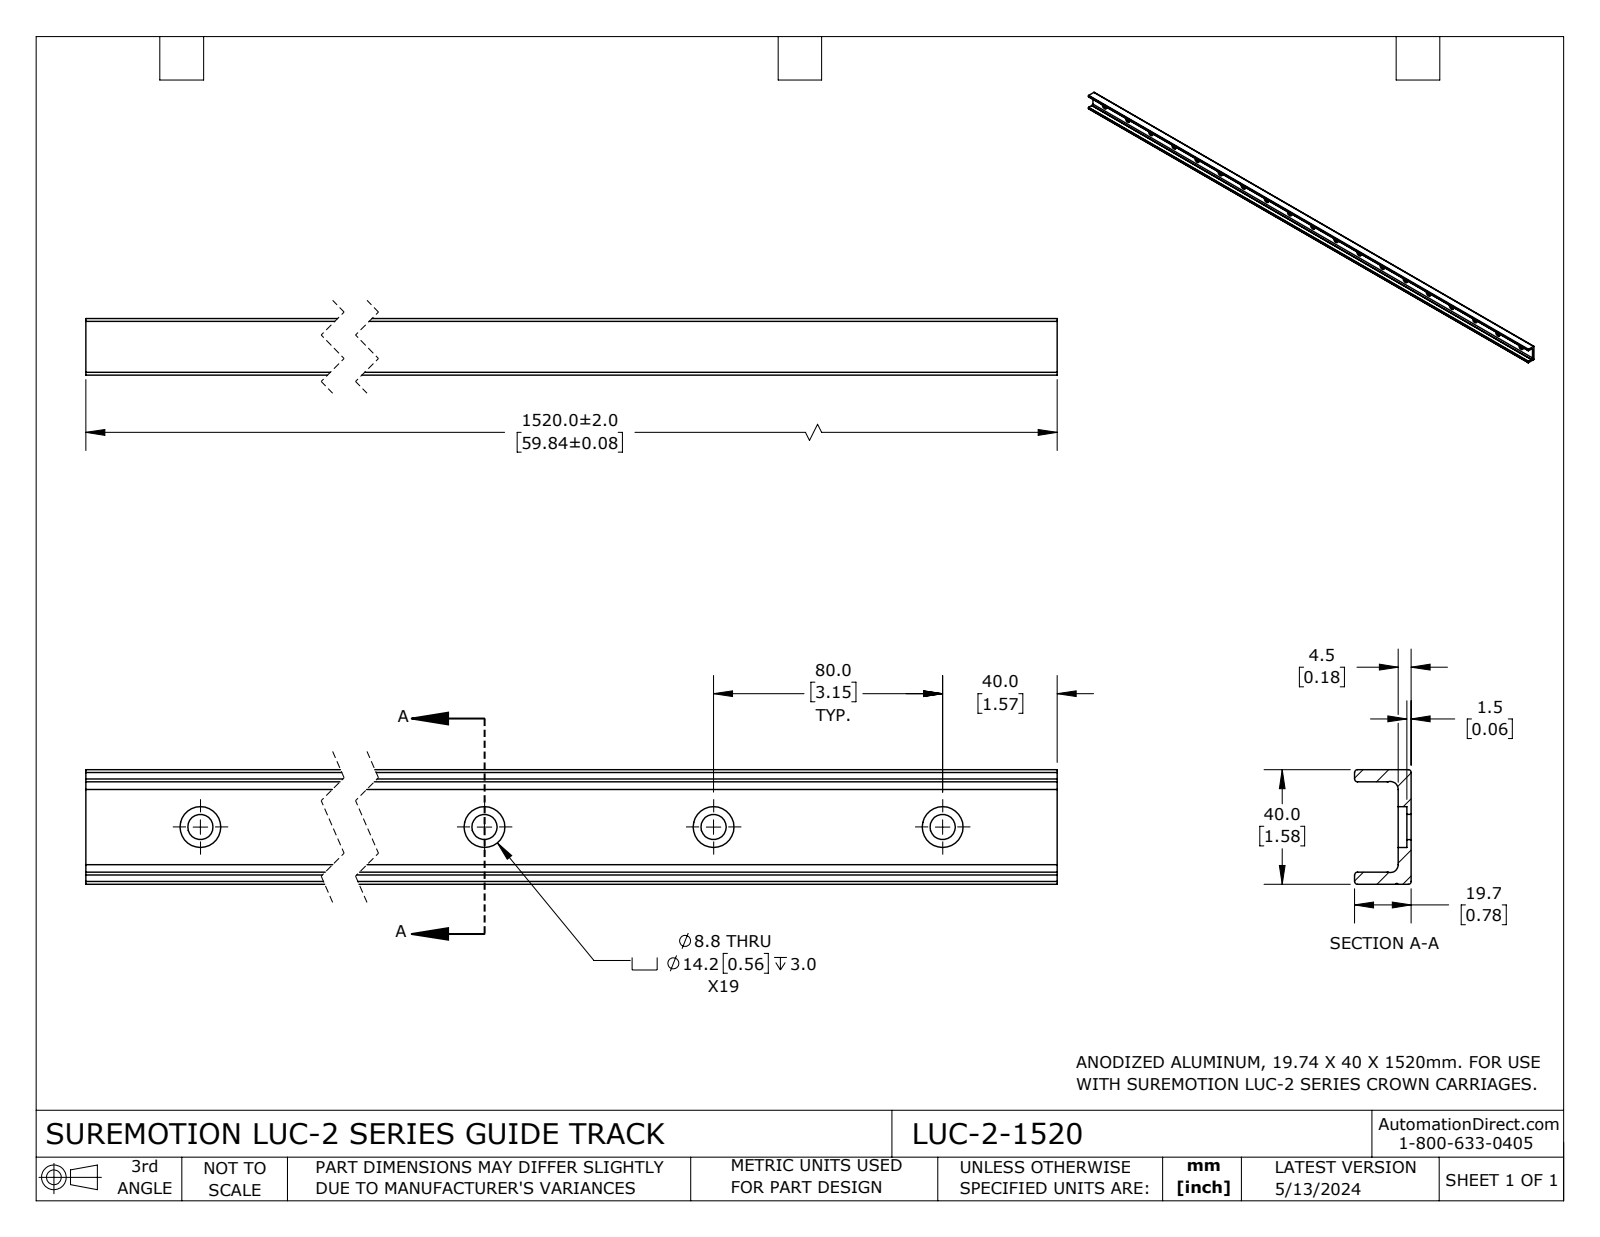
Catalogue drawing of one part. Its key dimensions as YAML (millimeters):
part_name: "LUC-2-1520"
step_written_by: "SolidWorks 2023 (CONFIG_CONTROL_DESIGN)"
units: millimeters
bodies: {solids: 1, faces: 117, planar: 30, cylindrical: 87, other: 0}
overall_size: [1520, 40, 19.7]
volume: 461300
surface_area: 223200
round_holes:
  - {diameter: 8.8, count: 19}
  - {diameter: 14.2, count: 19}
partial_cylinders:
  - {radius: 1, count: 8}
  - {radius: 2.8, count: 2}
  - {radius: 0.3, count: 1}
face_to_face_distances: [4.5, 4.3, 35.8, 40, 31.5, 19.7, 15.2, 1.5, 3, 18.2]
hole_center_spacings: [80, 160, 240, 320, 400, 480, 560, 640]
